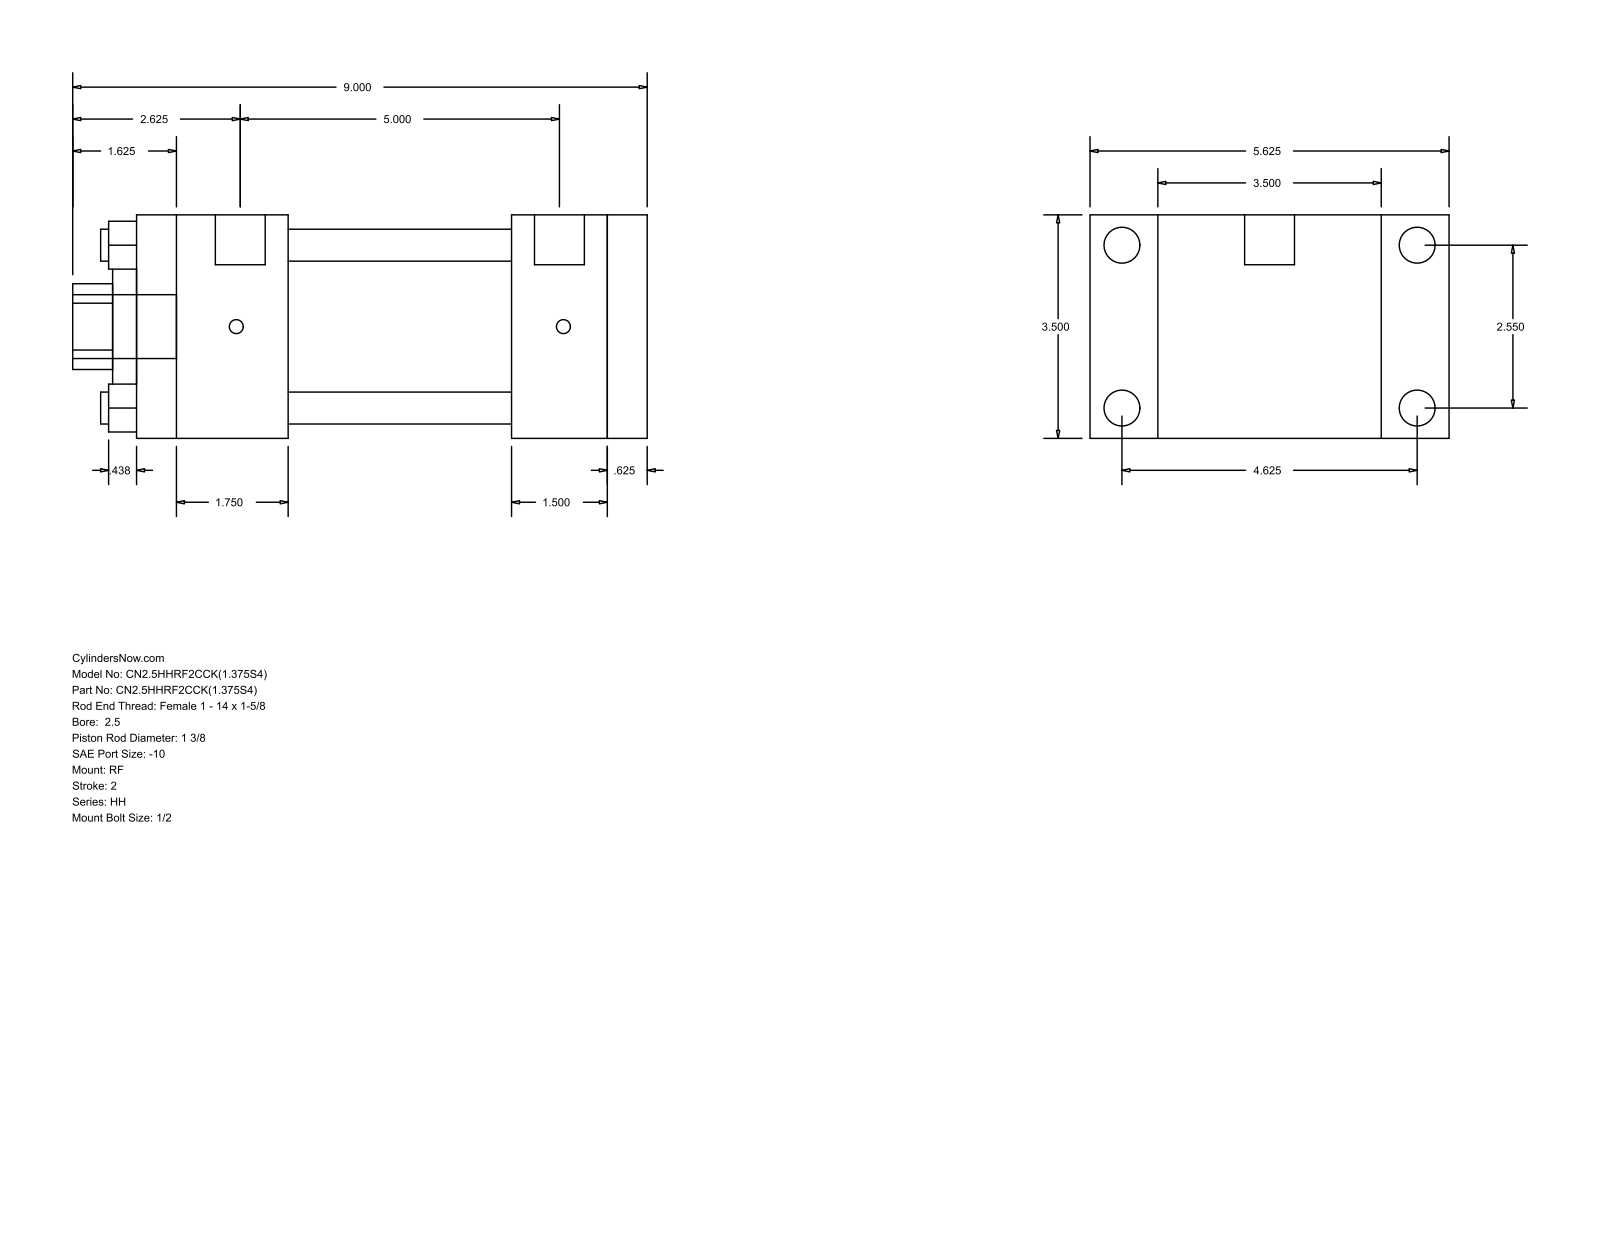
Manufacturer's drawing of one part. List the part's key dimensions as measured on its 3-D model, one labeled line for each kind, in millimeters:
Part name (STEP PRODUCT): HH_RF__0250_1.375
STEP written by: GSSL Pune (CONFIG_CONTROL_DESIGN)
Units: millimetres
Bodies: 0 solids, 92 faces (64 planar, 28 cylindrical, 0 other)
Overall size (bounding box): 228.6 × 142.88 × 88.9
Round holes (diameter × count): ⌀12.7 ×4, ⌀34.92 ×1, ⌀50.8 ×1, ⌀73.03 ×1
Round bosses / shafts (diameter × count): ⌀14.3 ×4, ⌀5.56 ×4, ⌀19.84 ×2, ⌀25.4 ×1
Partial cylindrical surfaces — rounded edges, fillets, slot ends (radius × count): R17.06 ×1
Main face-to-face distances: 88.9, 142.88, 203.2, 15.88, 187.32, 60.32, 127, 149.22, 38.1, 53.98
Hole centre spacings: 45.79, 64.76, 91.58
